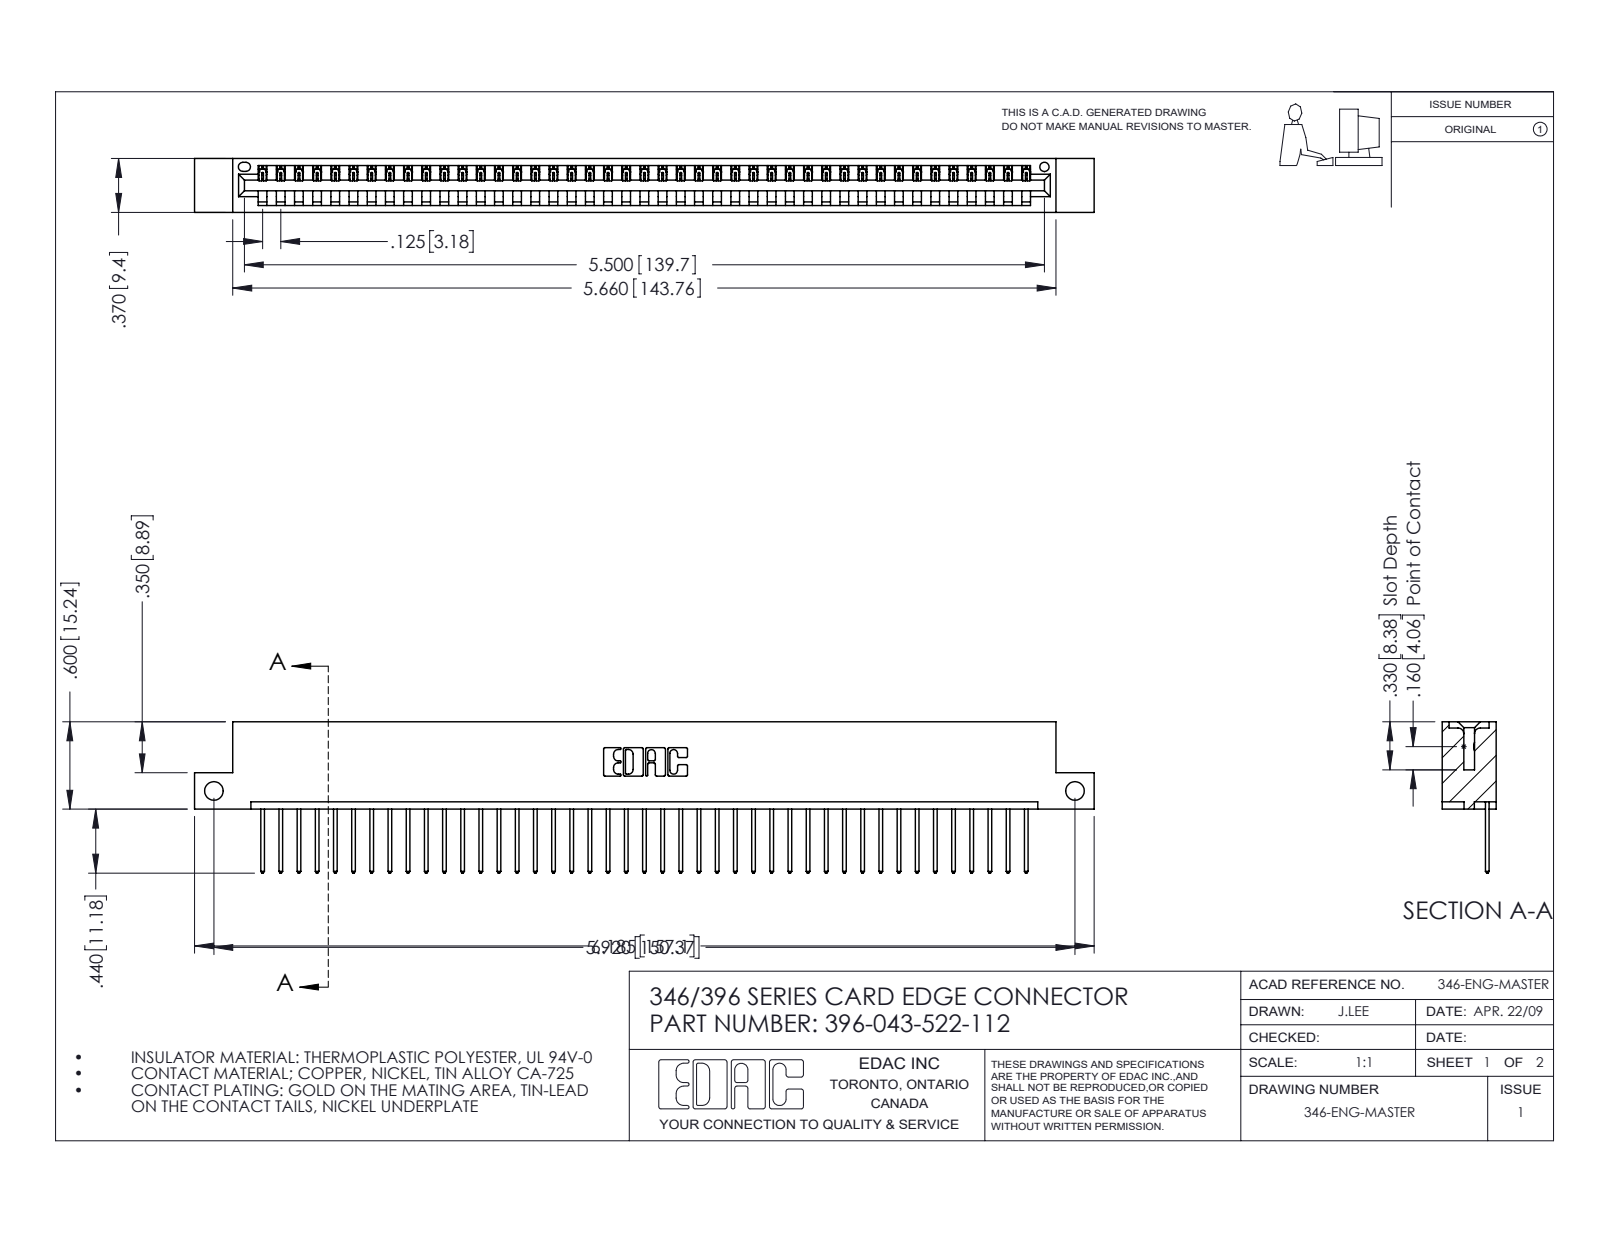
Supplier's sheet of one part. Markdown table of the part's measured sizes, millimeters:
| quantity | value |
| --- | --- |
| part name | 346 Part_Flush Mounting Lugs - Side Mount; 396-043-522-112; 345-292-001_345-293-122 |
| STEP written by | SolidWorks 2016 (CONFIG_CONTROL_DESIGN) |
| units | millimeters |
| bodies | 44 solids, 2616 faces (1796 planar, 820 cylindrical, 0 other) |
| overall size | 157.1 × 26.4 × 9.4 |
| volume | 15 000 mm³ |
| surface area | 18 720 mm² |
| round holes (diameter × count) | 3.3 × 2, 1.6 × 1 |
| partial cylindrical surfaces (radius × count) | 0.2 × 86, 0.3 × 86, 0.3 × 22, 0.2 × 6, 0.8 × 6, 0.7 × 3, 0.8 × 2, 1 × 2 |
| main face-to-face distances | 1.2, 8.2, 9.4, 6.4, 1.8, 7.6, 0.6, 3.8, 5.6, 2.5 |
| hole center spacings | 150.4 |
